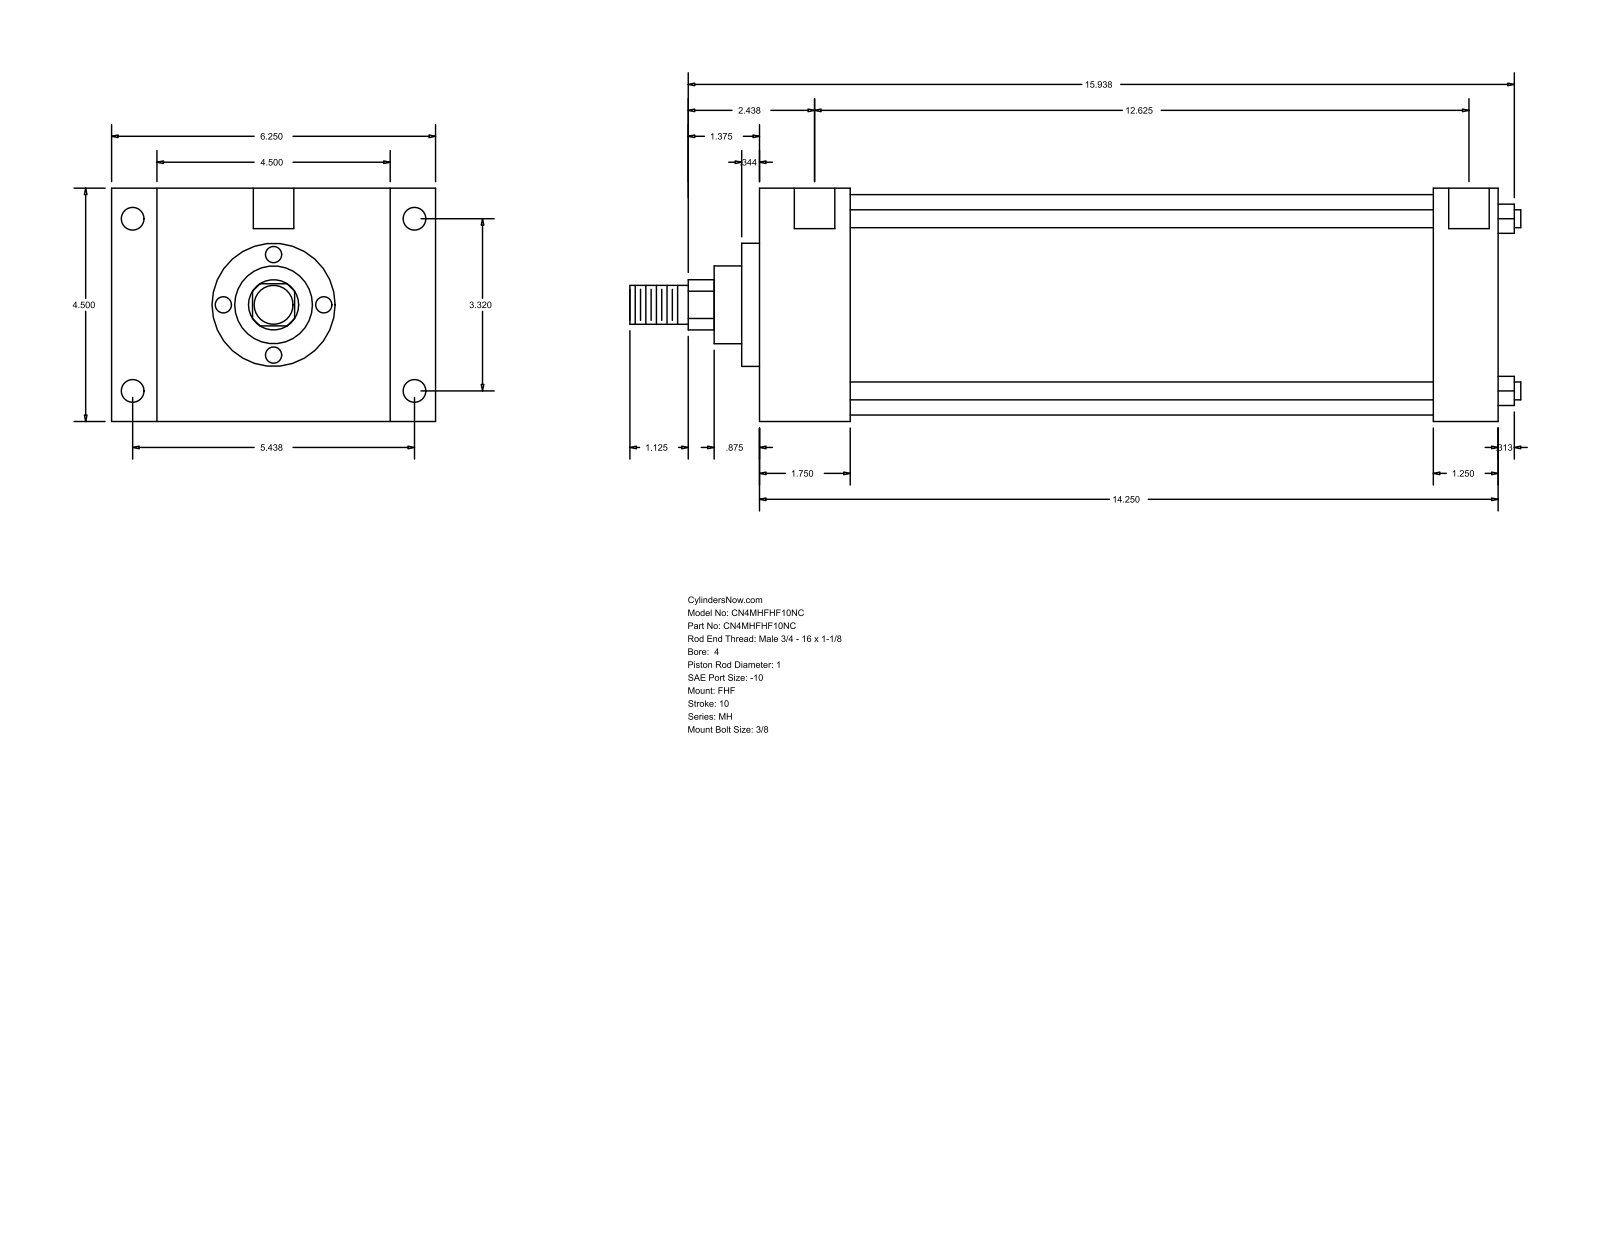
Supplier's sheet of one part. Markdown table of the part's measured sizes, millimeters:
| quantity | value |
| --- | --- |
| part name | MH_FHF__0400_1 |
| STEP written by | GSSL Pune (CONFIG_CONTROL_DESIGN) |
| units | millimeters |
| bodies | 0 solids, 90 faces (61 planar, 29 cylindrical, 0 other) |
| overall size | 436.56 × 158.75 × 114.3 |
| round holes (diameter × count) | 8.73 × 4, 11.13 × 4, 19.84 × 2 |
| round bosses / shafts (diameter × count) | 8.76 × 4, 107.95 × 1, 60.33 × 1, 38.1 × 1, 25.4 × 1, 19.05 × 1 |
| partial cylindrical surfaces (radius × count) | 12.29 × 1 |
| main face-to-face distances | 114.3, 361.96, 44.46, 317.5, 22.23, 136.53, 158.76, 330.2, 285.74, 31.76 |
| hole center spacings | 84.32, 138.12, 161.82, 323.85, 1.58, 1.59, 320.68, 322.26 |
